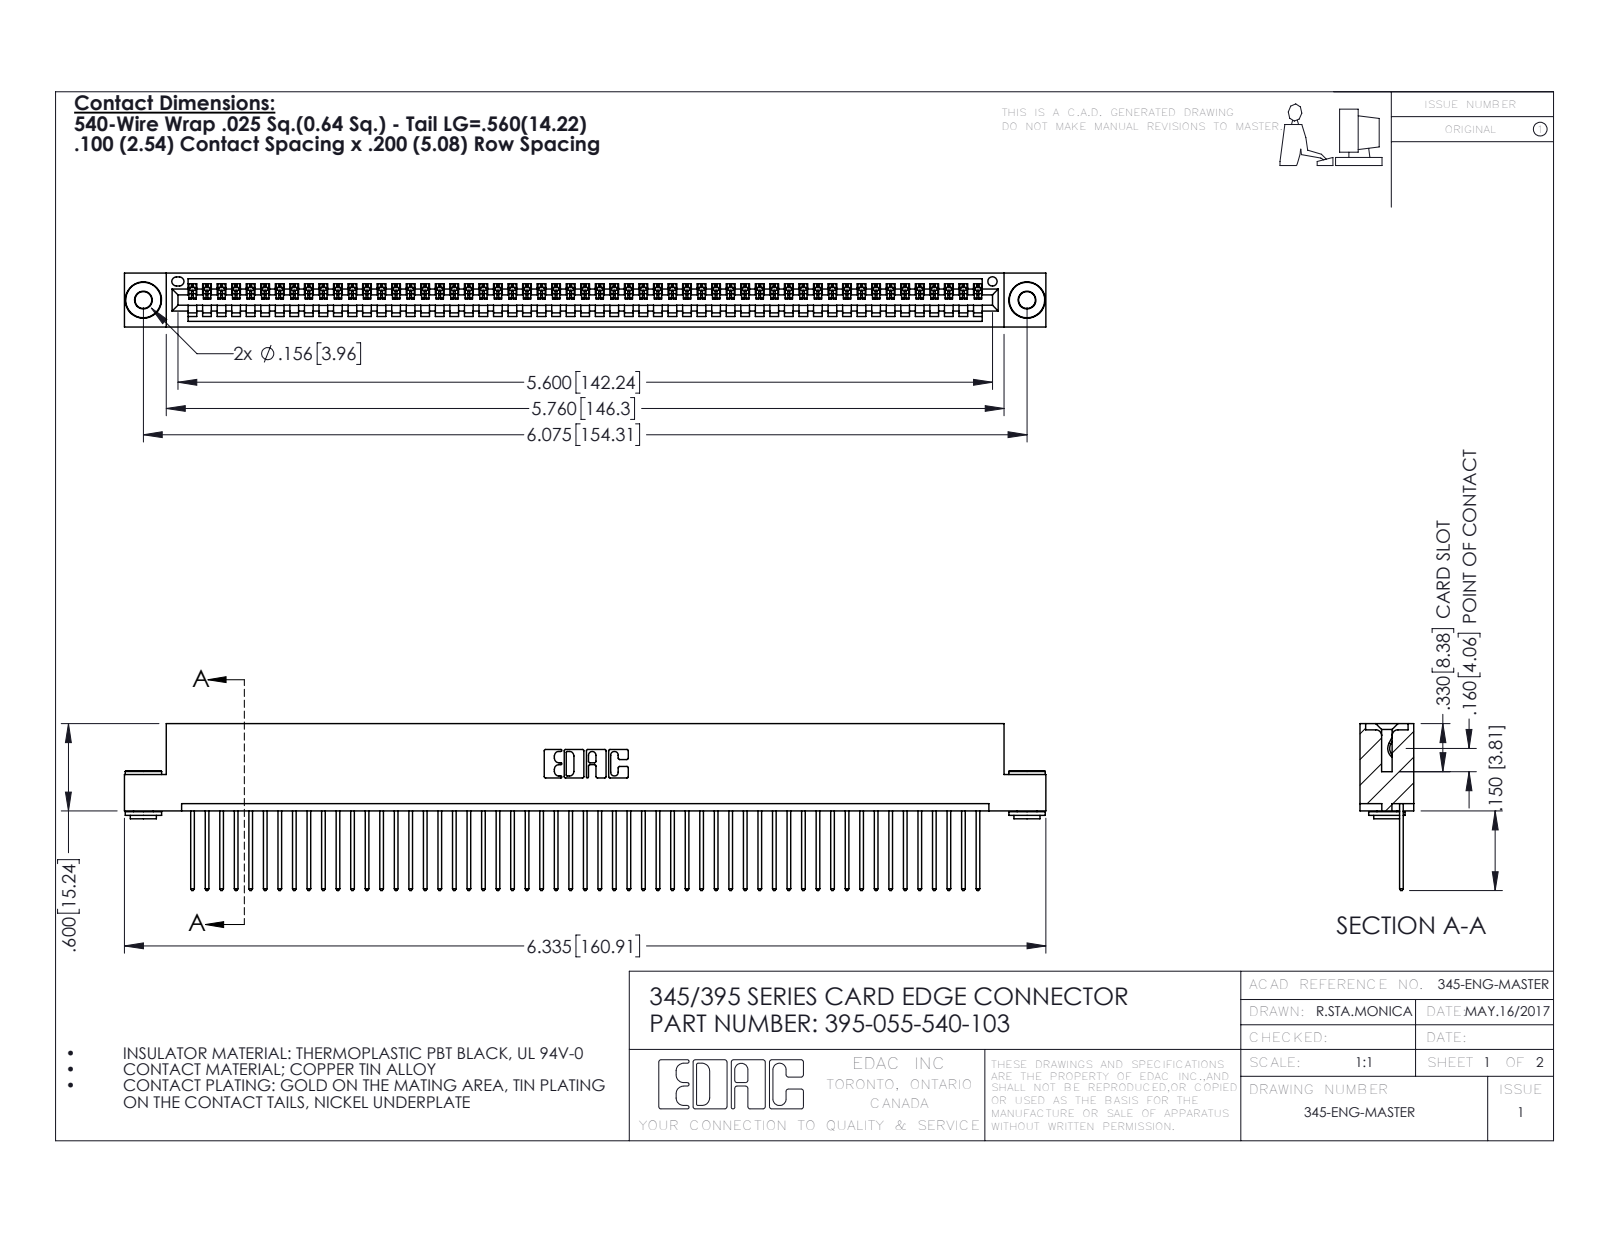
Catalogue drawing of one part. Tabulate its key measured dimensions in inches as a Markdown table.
| quantity | value |
| --- | --- |
| part name | 395-055-540-103; 345-250-002_345-250-002-102; 345 Part_Flush Mounting Lugs - 0.156 Dia-TH; 345-292-001_345-293-140 |
| STEP written by | SolidWorks 2016 (CONFIG_CONTROL_DESIGN) |
| units | inches |
| bodies | 58 solids, 3354 faces (2290 planar, 1056 cylindrical, 8 other) |
| overall size | 6.335 × 1.147 × 0.37 |
| volume | 0.945 in³ |
| surface area | 33.33 in² |
| round holes (diameter × count) | 0.116 × 2, 0.156 × 2, 0.064 × 1 |
| round bosses / shafts (diameter × count) | 0.25 × 2, 0.18 × 2, 0.136 × 2 |
| partial cylindrical surfaces (radius × count) | 0.006 × 110, 0.01 × 110, 0.01 × 22, 0.007 × 6, 0.031 × 6, 0.026 × 3, 0.031 × 2, 0.04 × 2 |
| main face-to-face distances | 0.072, 0.298, 0.37, 0.025, 0.098, 0.272, 0.2, 0.225, 0.149, 0.072 |
| hole center spacings | 0.27, 5.839, 6.075 |
